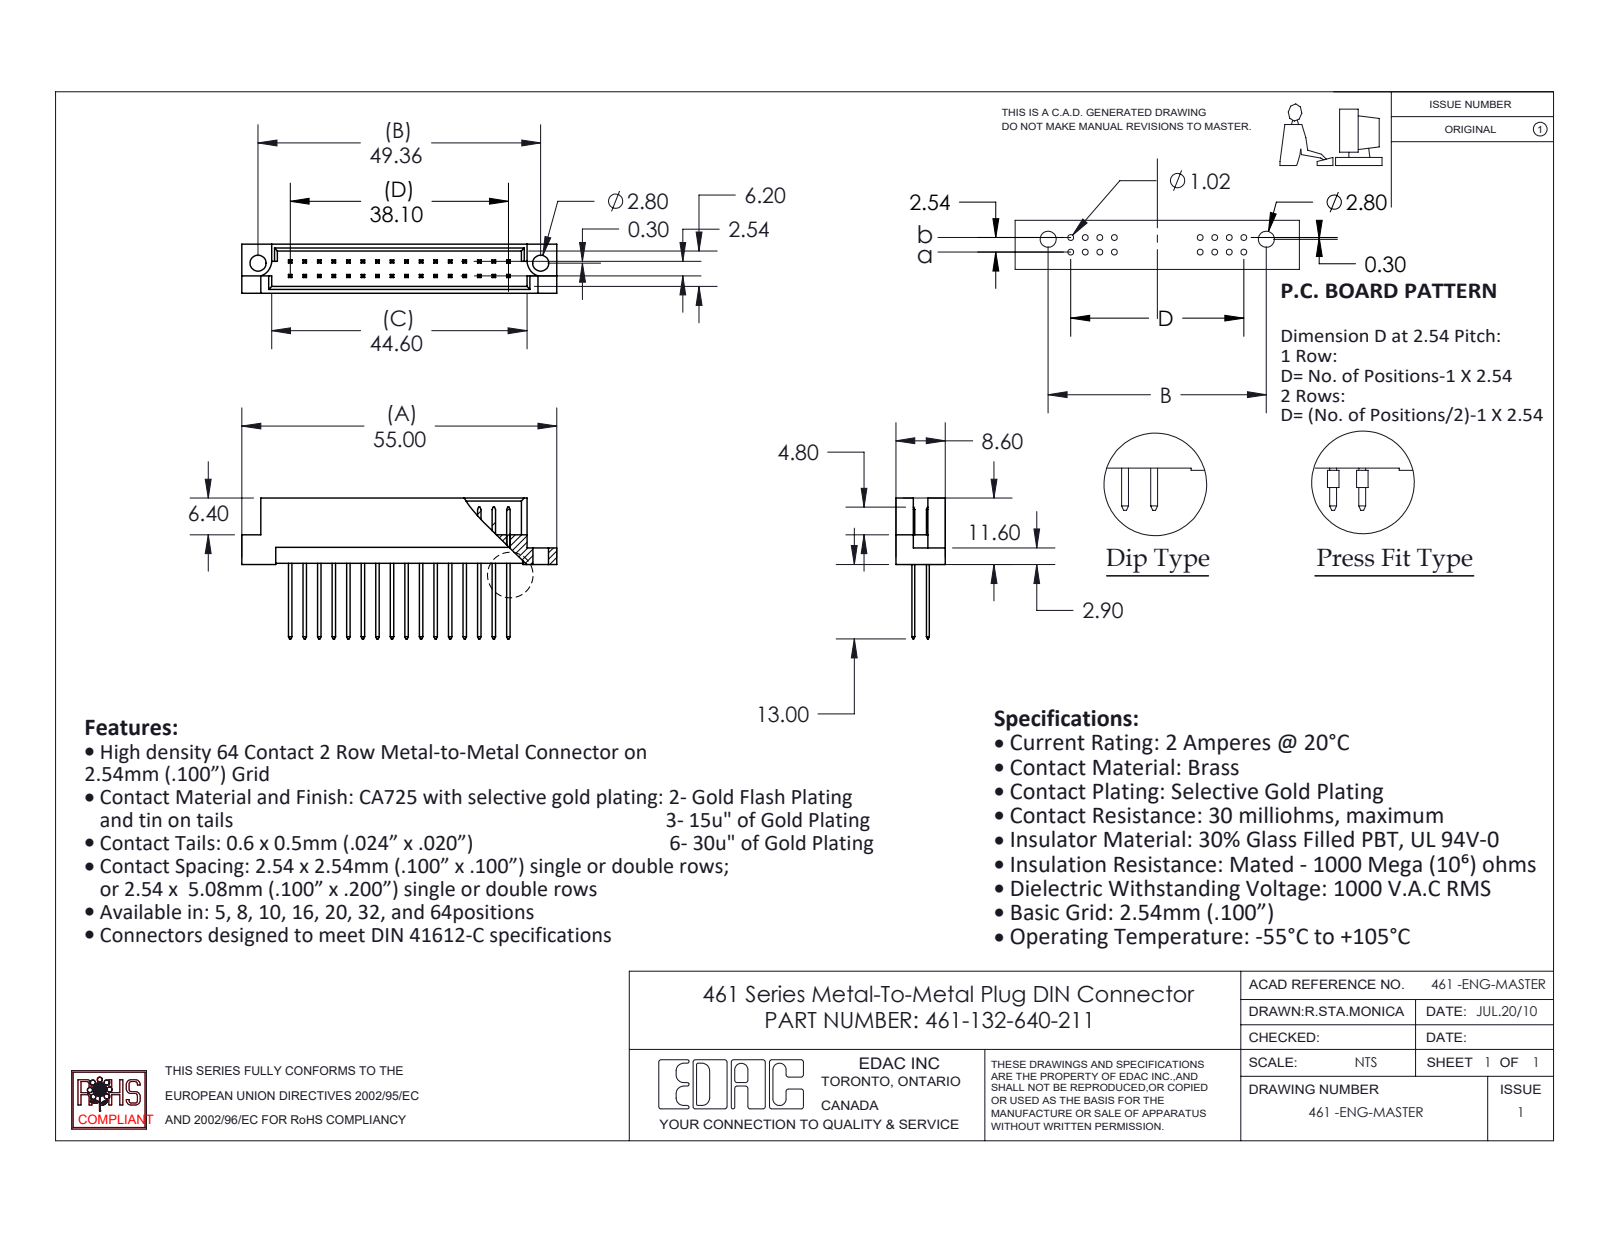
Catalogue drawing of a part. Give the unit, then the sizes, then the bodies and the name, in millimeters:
Units: millimetres
Overall size (bounding box): 55 × 24.6 × 8.6
Round holes (diameter × count): ⌀2.8 ×2
Partial cylindrical surfaces — rounded edges, fillets, slot ends (radius × count): R2.8 ×2
Main face-to-face distances: 2.54, 1.2, 7.4, 2.78, 5.82, 1.58, 4.62, 3.28, 5.32, 2.08
Hole centre spacings: 49.36
Volume: 2 871 mm³ · Surface area: 4 854 mm²
Bodies: 33 solids, 624 faces (618 planar, 6 cylindrical, 0 other)
Part name (STEP PRODUCT): 461-290_40; 461 Part_32; 461-132-640-211
STEP written by: SolidWorks 2020 (CONFIG_CONTROL_DESIGN)
